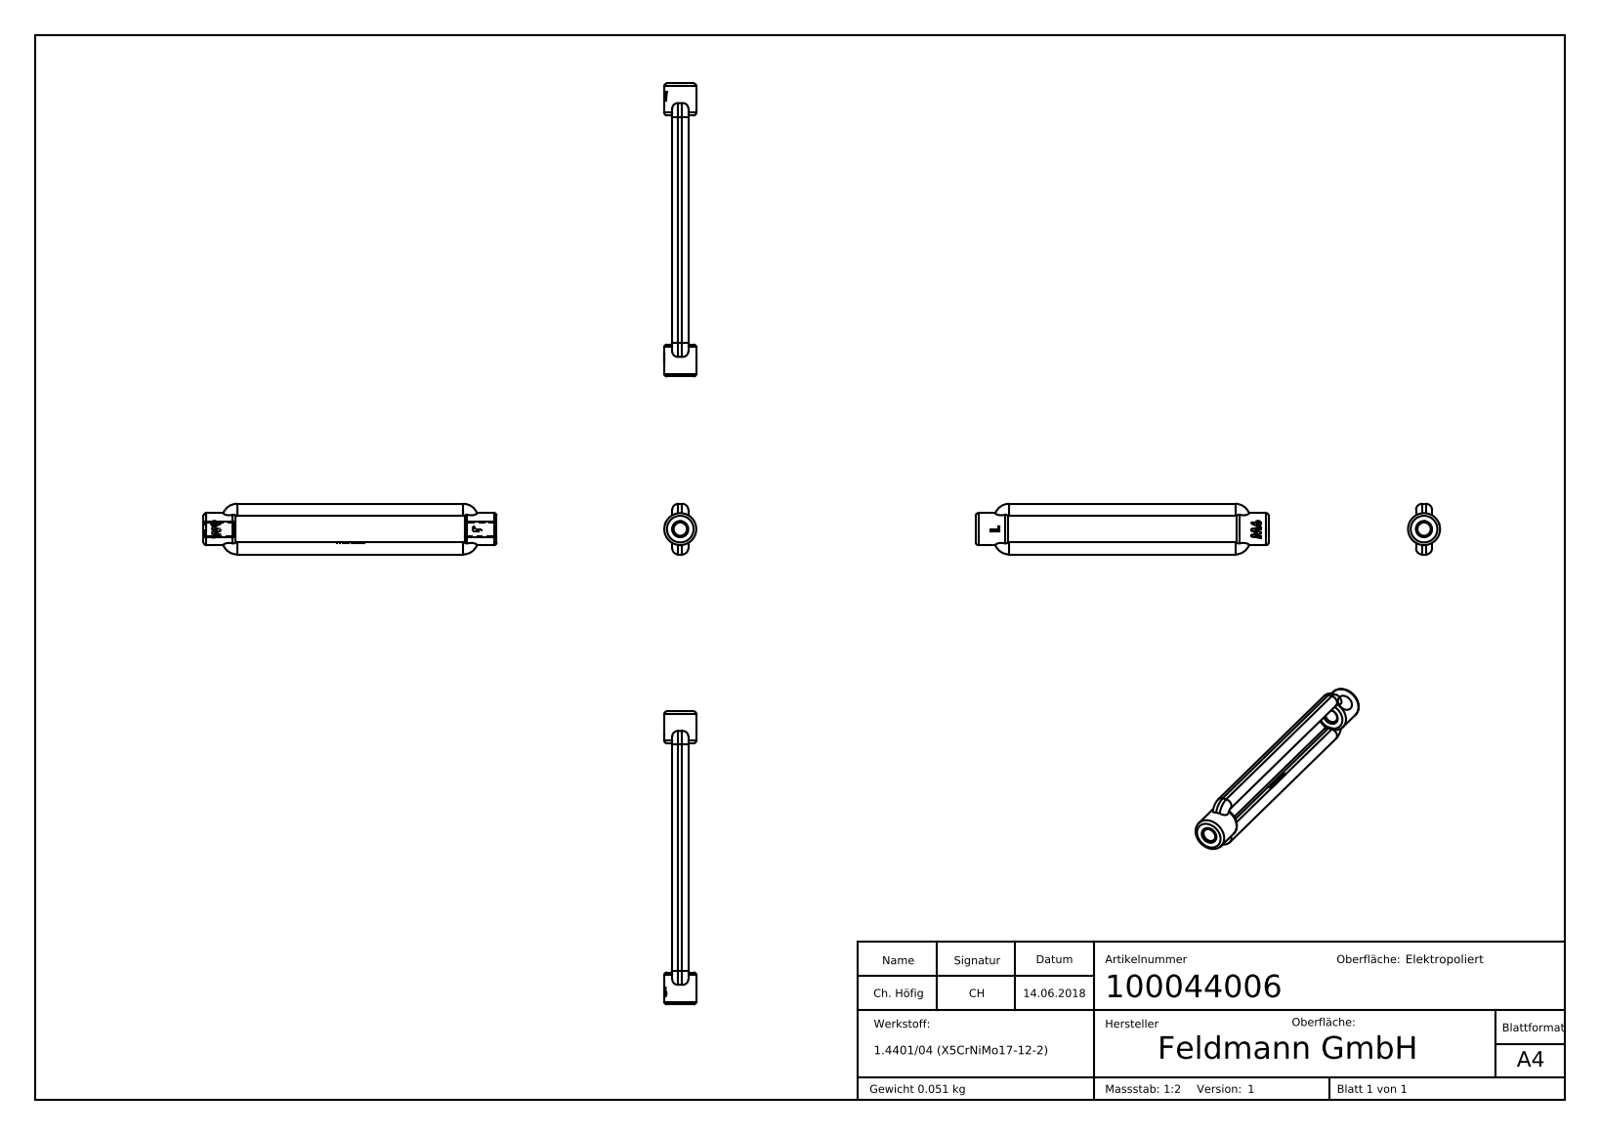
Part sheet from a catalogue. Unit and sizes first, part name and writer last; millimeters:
Units: millimetres
Overall size (bounding box): 110 × 19 × 12
Round holes (diameter × count): ⌀5 ×1
Round bosses / shafts (diameter × count): ⌀12 ×1
Partial cylindrical surfaces — rounded edges, fillets, slot ends (radius × count): R1 ×4, R2.25 ×4, R5.5 ×4, R5.98 ×1
Main face-to-face distances: 4.5, 14.5, 19, 10, 12, 98, 110, 86, 4.4, 10.1
Volume: 6 349 mm³ · Surface area: 4 632 mm²
Bodies: 1 solid, 307 faces (136 planar, 24 cylindrical, 147 other)
Part name (STEP PRODUCT): 100044006
STEP written by: SolidWorks 2015 (CONFIG_CONTROL_DESIGN)
